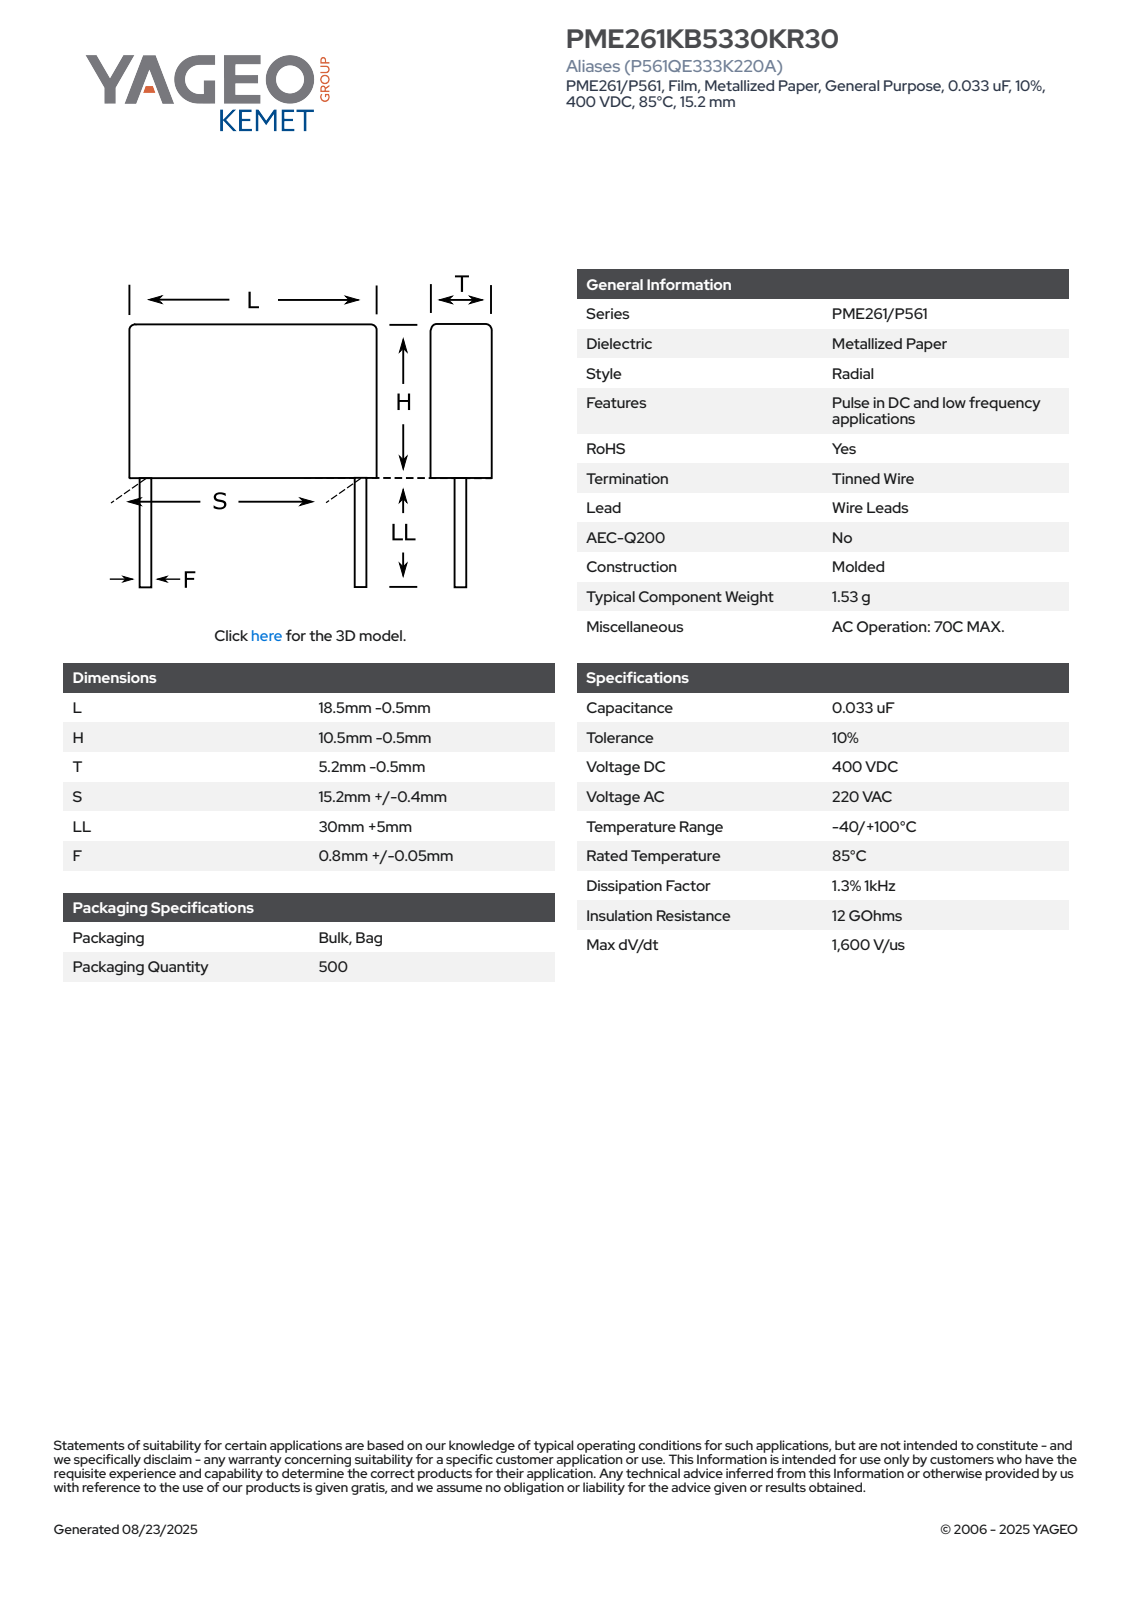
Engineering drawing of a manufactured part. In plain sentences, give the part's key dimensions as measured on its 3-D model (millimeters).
The part is named "CFR_MOLDED_18.5X10.5X5.2_L18H10T4.7S15.2LL35F0.85". Its 3-D file was written by "SolidWorks 2014 (AUTOMOTIVE_DESIGN)". It is 4 solids with 73 faces: 65 planar, 8 cylindrical and 0 other. Overall it measures 45 by 18 by 4.71 millimeters. Its volume is 883 cubic millimeters and its surface area 816 square millimeters. Round bosses or shafts: 2 of diameter 0.85. Partial cylindrical surfaces (rounded edges, fillets, slot ends): 4 of radius 0.5. The main face-to-face distances are 4.7, 10, 18, 4.71, 35, 45, 4.19, 5.81, 40.81, 39.19.
